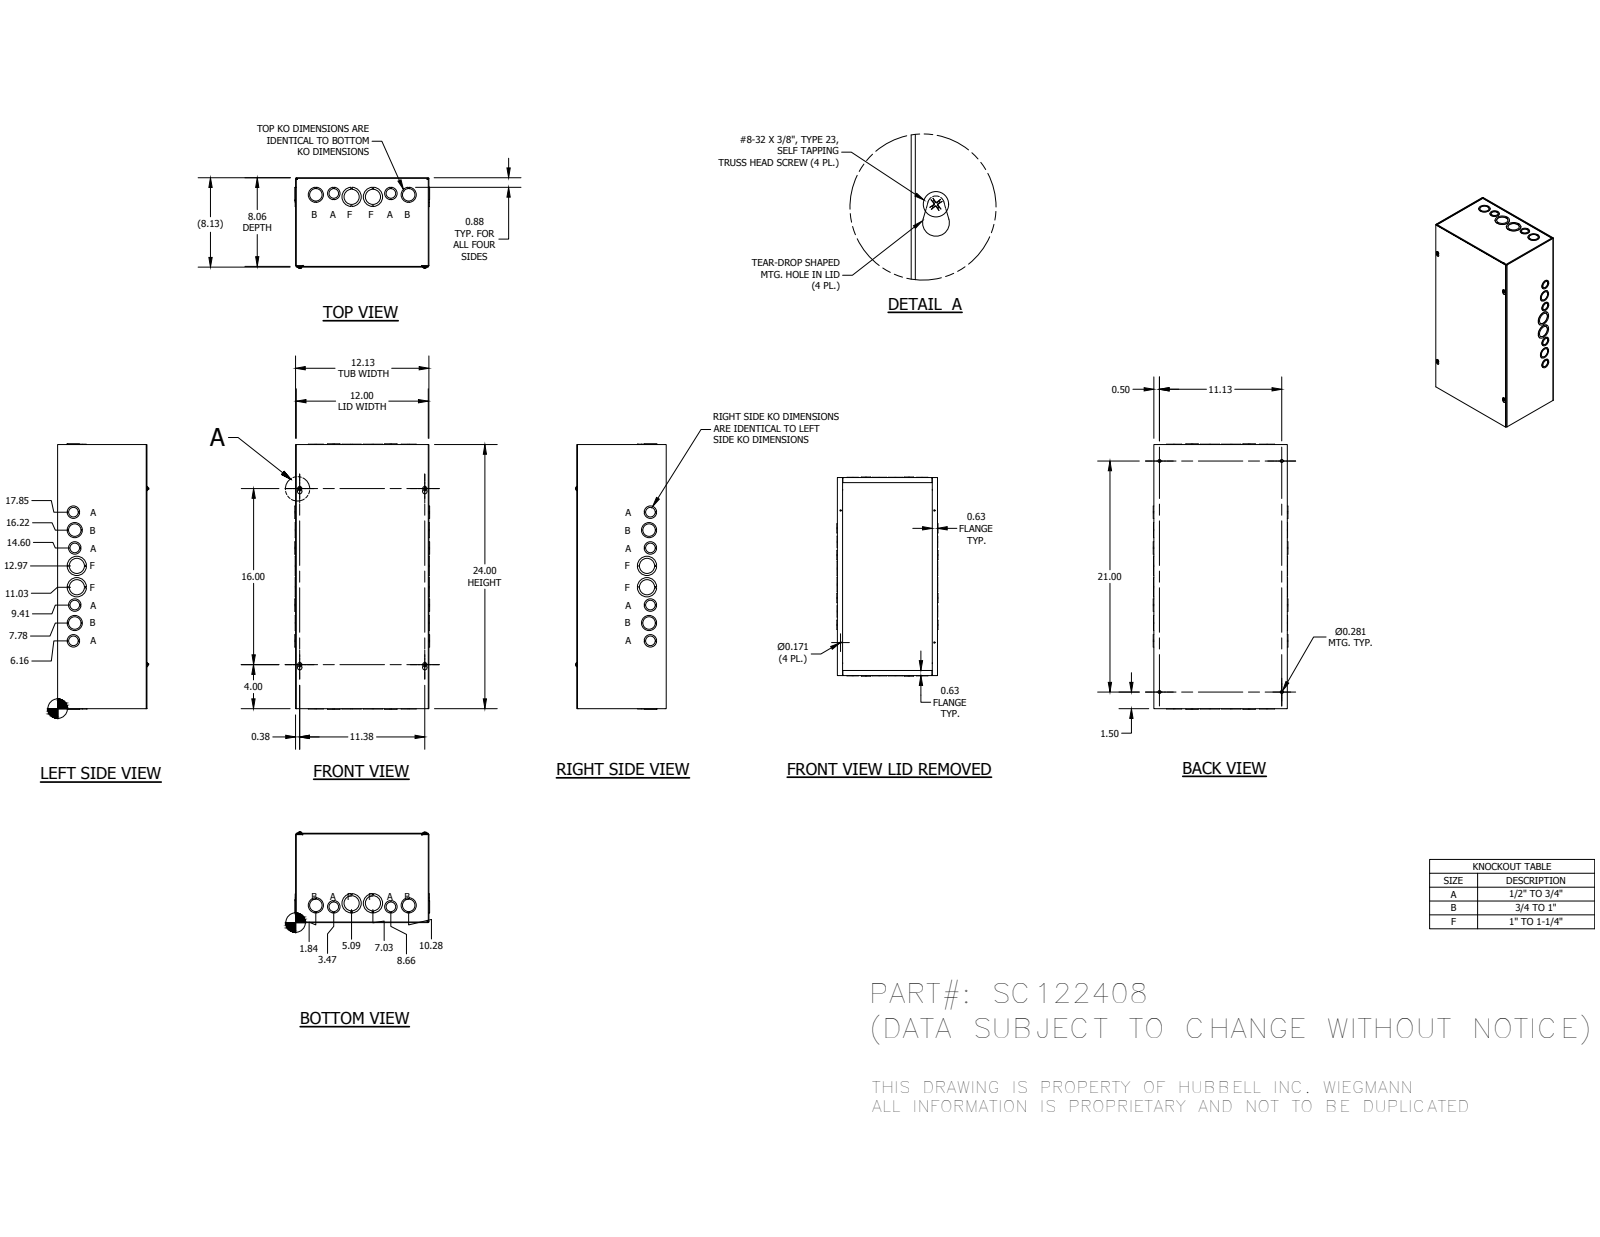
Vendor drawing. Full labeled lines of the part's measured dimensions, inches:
Part name (STEP PRODUCT): SC122408BLR; SC1208TB; SC1224LPA; 34056 (+1 more)
STEP written by: Autodesk Inventor 2014 (AUTOMOTIVE_DESIGN)
Units: inches
Bodies: 29 solids, 1055 faces (771 planar, 216 cylindrical, 68 other)
Overall size (bounding box): 24.125 × 12.25 × 8.225
Round holes (diameter × count): ⌀1.125 ×12, ⌀0.875 ×8, ⌀1.375 ×8, ⌀0.171 ×4, ⌀0.281 ×4, ⌀1.75 ×4
Round bosses / shafts (diameter × count): ⌀0.384 ×4, ⌀0.164 ×4
Partial cylindrical surfaces — rounded edges, fillets, slot ends (radius × count): R0.031 ×12, R0.094 ×12, R0.125 ×4, R0.203 ×4
Main face-to-face distances: 0.063, 8.063, 12.063, 8, 8.125, 12, 12.125, 23.937, 24, 23.875
Hole centre spacings: 1.63, 1.655, 2.503, 3.256, 3.579, 5.194, 6.816, 11.524
